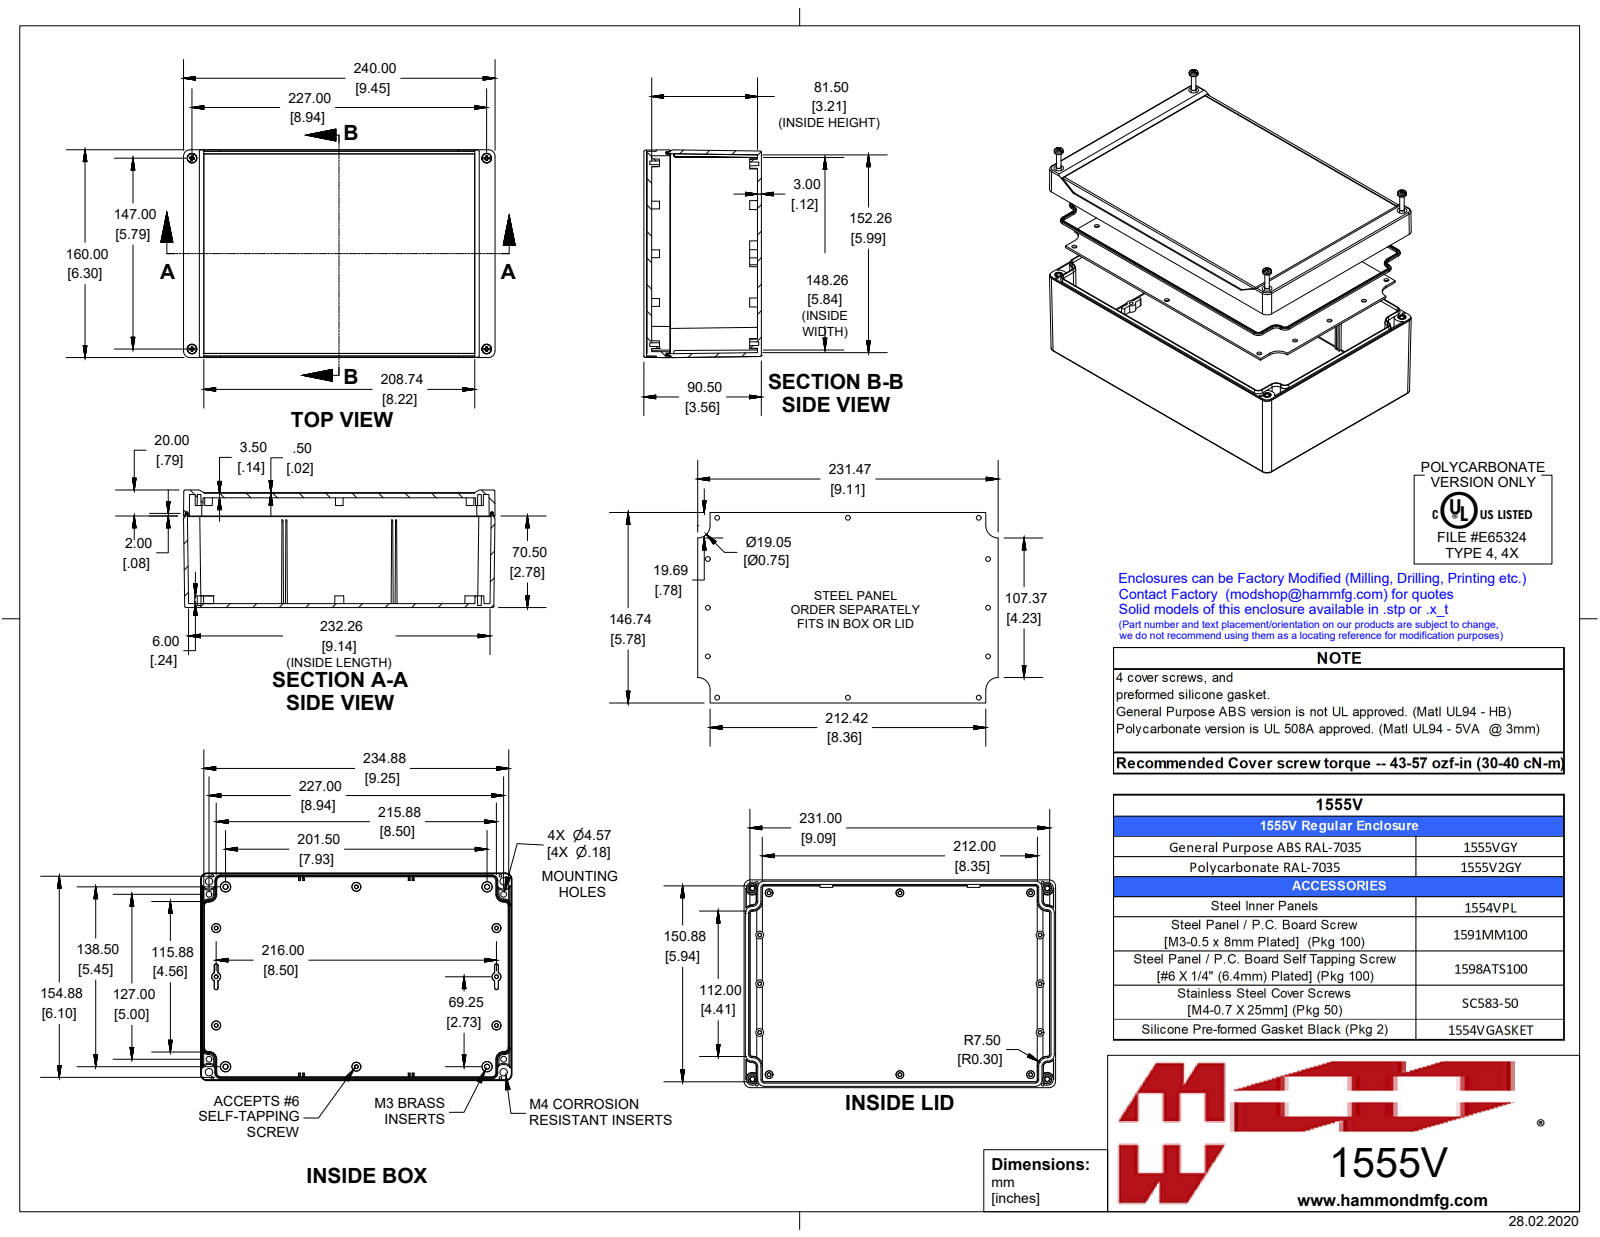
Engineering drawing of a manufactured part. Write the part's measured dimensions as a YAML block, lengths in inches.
part_name: "1555V2GY"
step_written_by: "SolidWorks 2019 (AUTOMOTIVE_DESIGN)"
units: inches
bodies: {solids: 15, faces: 1460, planar: 474, cylindrical: 334, other: 652}
overall_size: [9.449, 6.299, 3.563]
volume: 29.56
surface_area: 506.8
round_holes:
  - {diameter: 0.079, count: 8}
  - {diameter: 0.097, count: 4}
  - {diameter: 0.128, count: 4}
  - {diameter: 0.138, count: 4}
  - {diameter: 0.276, count: 4}
round_bosses_or_shafts:
  - {diameter: 0.236, count: 6}
  - {diameter: 0.272, count: 4}
  - {diameter: 0.25, count: 4}
  - {diameter: 0.218, count: 4}
  - {diameter: 0.21, count: 4}
  - {diameter: 0.19, count: 4}
  - {diameter: 0.154, count: 4}
  - {diameter: 0.152, count: 4}
partial_cylinders:
  - {radius: 0.02, count: 32}
  - {radius: 0.039, count: 8}
  - {radius: 0.197, count: 8}
  - {radius: 0.187, count: 4}
  - {radius: 0.059, count: 2}
face_to_face_distances: [0.118, 0.138, 3.327, 3.209, 3.465, 3.346, 0.059, 0.177, 0.098, 0.039]
hole_center_spacings: [0.197, 0.526, 0.529, 5.643, 5.805, 5.959, 6.128, 6.129]
